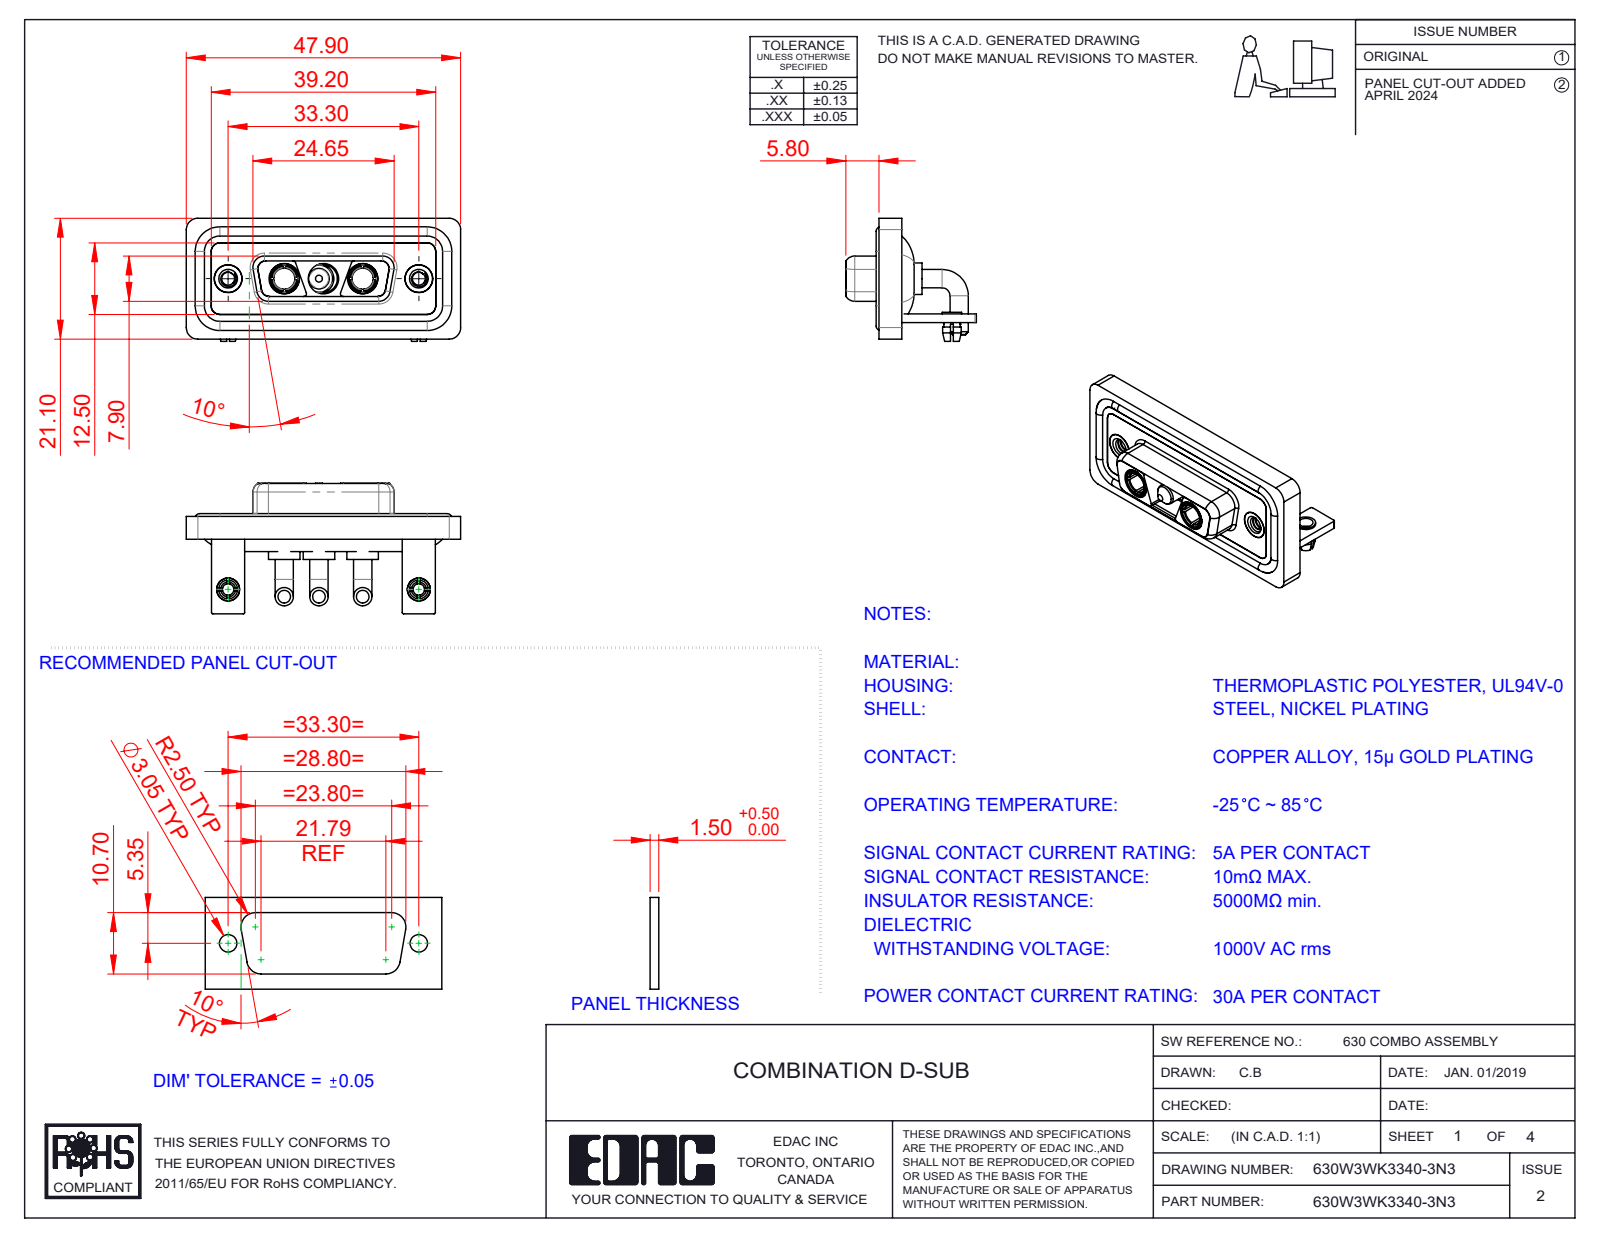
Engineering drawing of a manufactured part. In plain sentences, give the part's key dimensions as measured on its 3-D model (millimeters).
The part is named "630Combo Housing_3WK3; 630W3WK3340-3N3; 630Combo Board Lock_50 Contacts; Power Pin_30A RA (+6 more)". Its 3-D file was written by "SolidWorks 2023 (CONFIG_CONTROL_DESIGN)". It is 17 solids with 735 faces: 246 planar, 320 cylindrical and 169 other. Overall it measures 47.9 by 22.8 by 21.5 millimeters. Its volume is 6 519 cubic millimeters and its surface area 10 739 square millimeters. Round holes: 5 of diameter 4.85, 3 of diameter 5.3, 2 of diameter 2, 2 of diameter 2.26, 2 of diameter 2.5, 2 of diameter 3.2, 2 of diameter 3.7, 2 of diameter 4, 2 of diameter 4.05, 2 of diameter 5. Round bosses or shafts: 6 of diameter 3.2, 4 of diameter 1.6, 3 of diameter 5.5, 3 of diameter 5.2, 3 of diameter 4.75, 3 of diameter 3.75, 2 of diameter 4.96, 2 of diameter 4.95. Partial cylindrical surfaces (rounded edges, fillets, slot ends): 21 of radius 2, 18 of radius 1.5, 16 of radius 0.25, 12 of radius 1.35, 9 of radius 0.5, 8 of radius 1.6, 4 of radius 0.6, 4 of radius 0.65. The main face-to-face distances are 0.4, 2.9, 1.5, 3.7, 1.8, 1.1, 4.1, 1.6, 2.5, 1.4. The hole center spacings are 6.85, 9.8, 16.65, 23.5, 33.3, 13.7.
